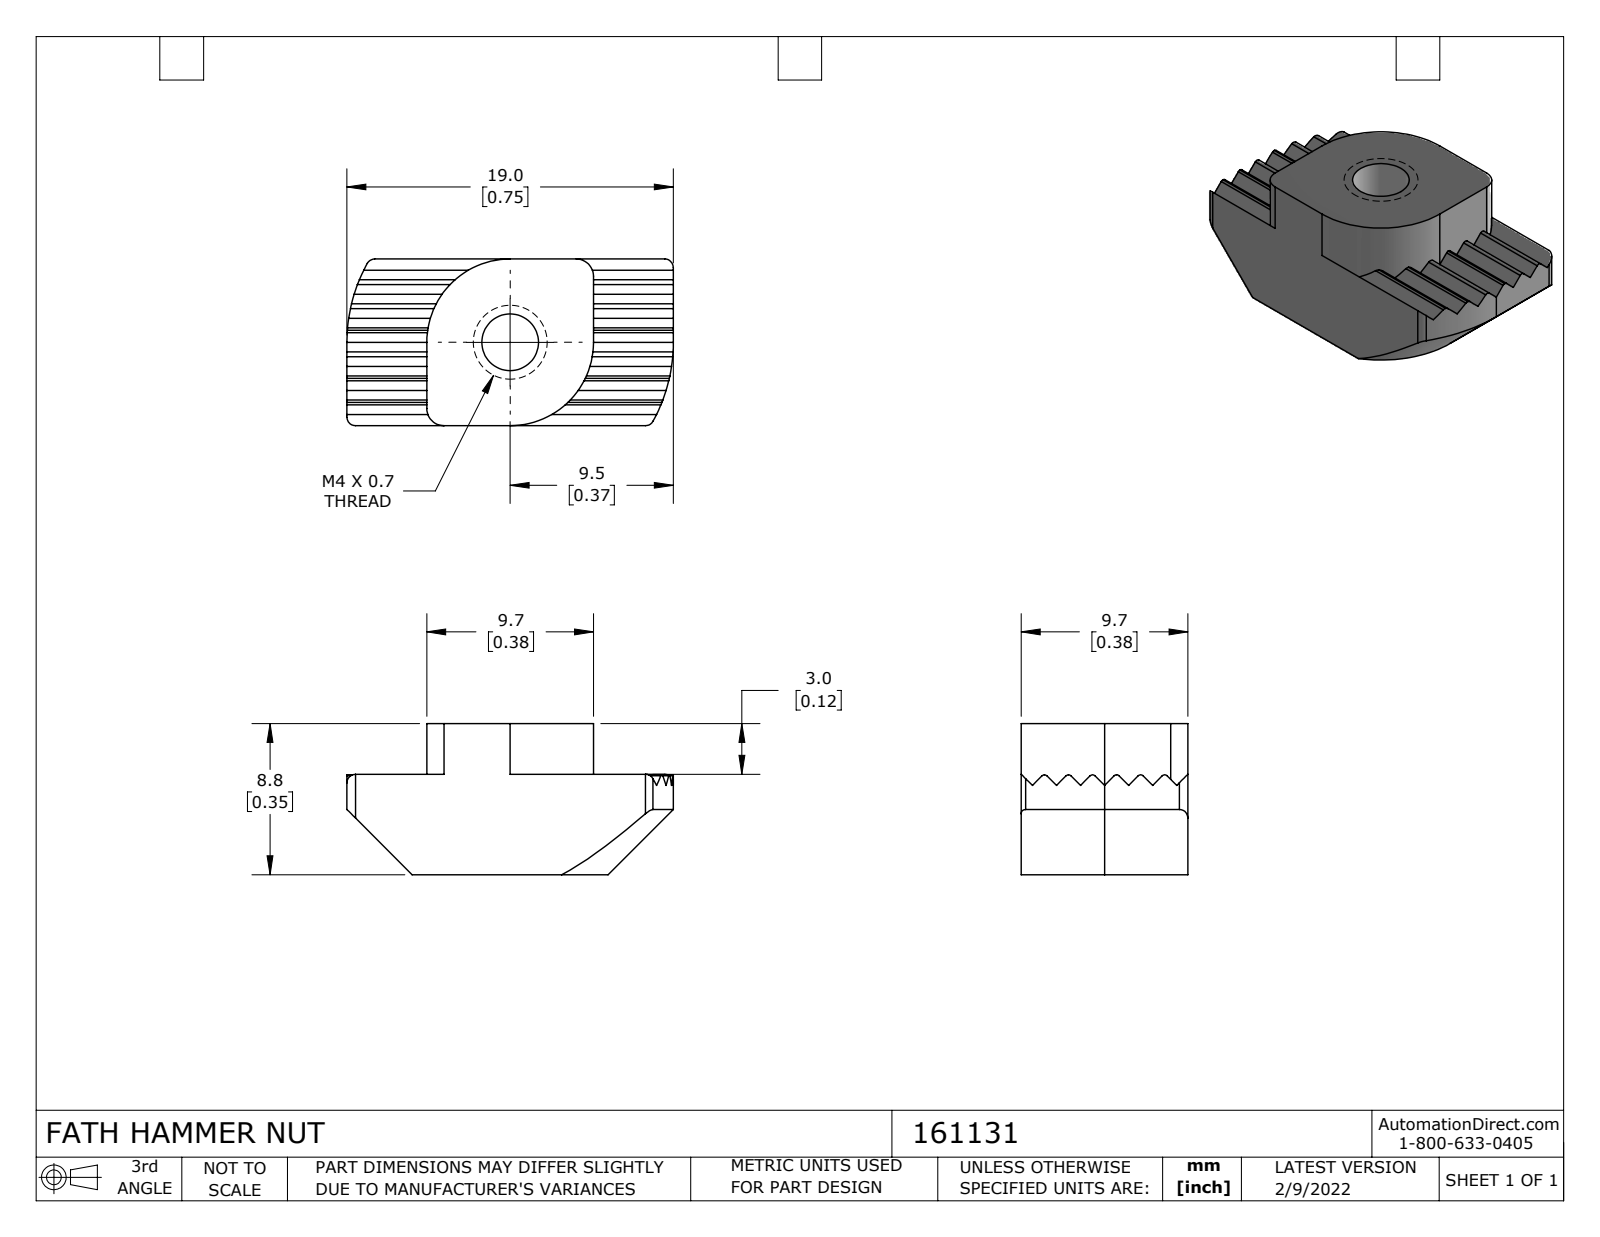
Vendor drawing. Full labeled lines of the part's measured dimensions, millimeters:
Part name (STEP PRODUCT): 161131
STEP written by: SolidWorks 2021 (CONFIG_CONTROL_DESIGN)
Units: millimetres
Bodies: 1 solid, 70 faces (38 planar, 30 cylindrical, 2 other)
Overall size (bounding box): 19 × 9.7 × 8.8
Volume: 1 049 mm³ · Surface area: 815 mm²
Round holes (diameter × count): ⌀3.3 ×1
Partial cylindrical surfaces — rounded edges, fillets, slot ends (radius × count): R0.2 ×6, R0.5 ×4, R1 ×2, R4.85 ×1, R9.5 ×1
Main face-to-face distances: 9.7, 0.99, 8.8, 1.98, 2.97, 3.96, 4.95, 5.94, 4.65, 14.35
